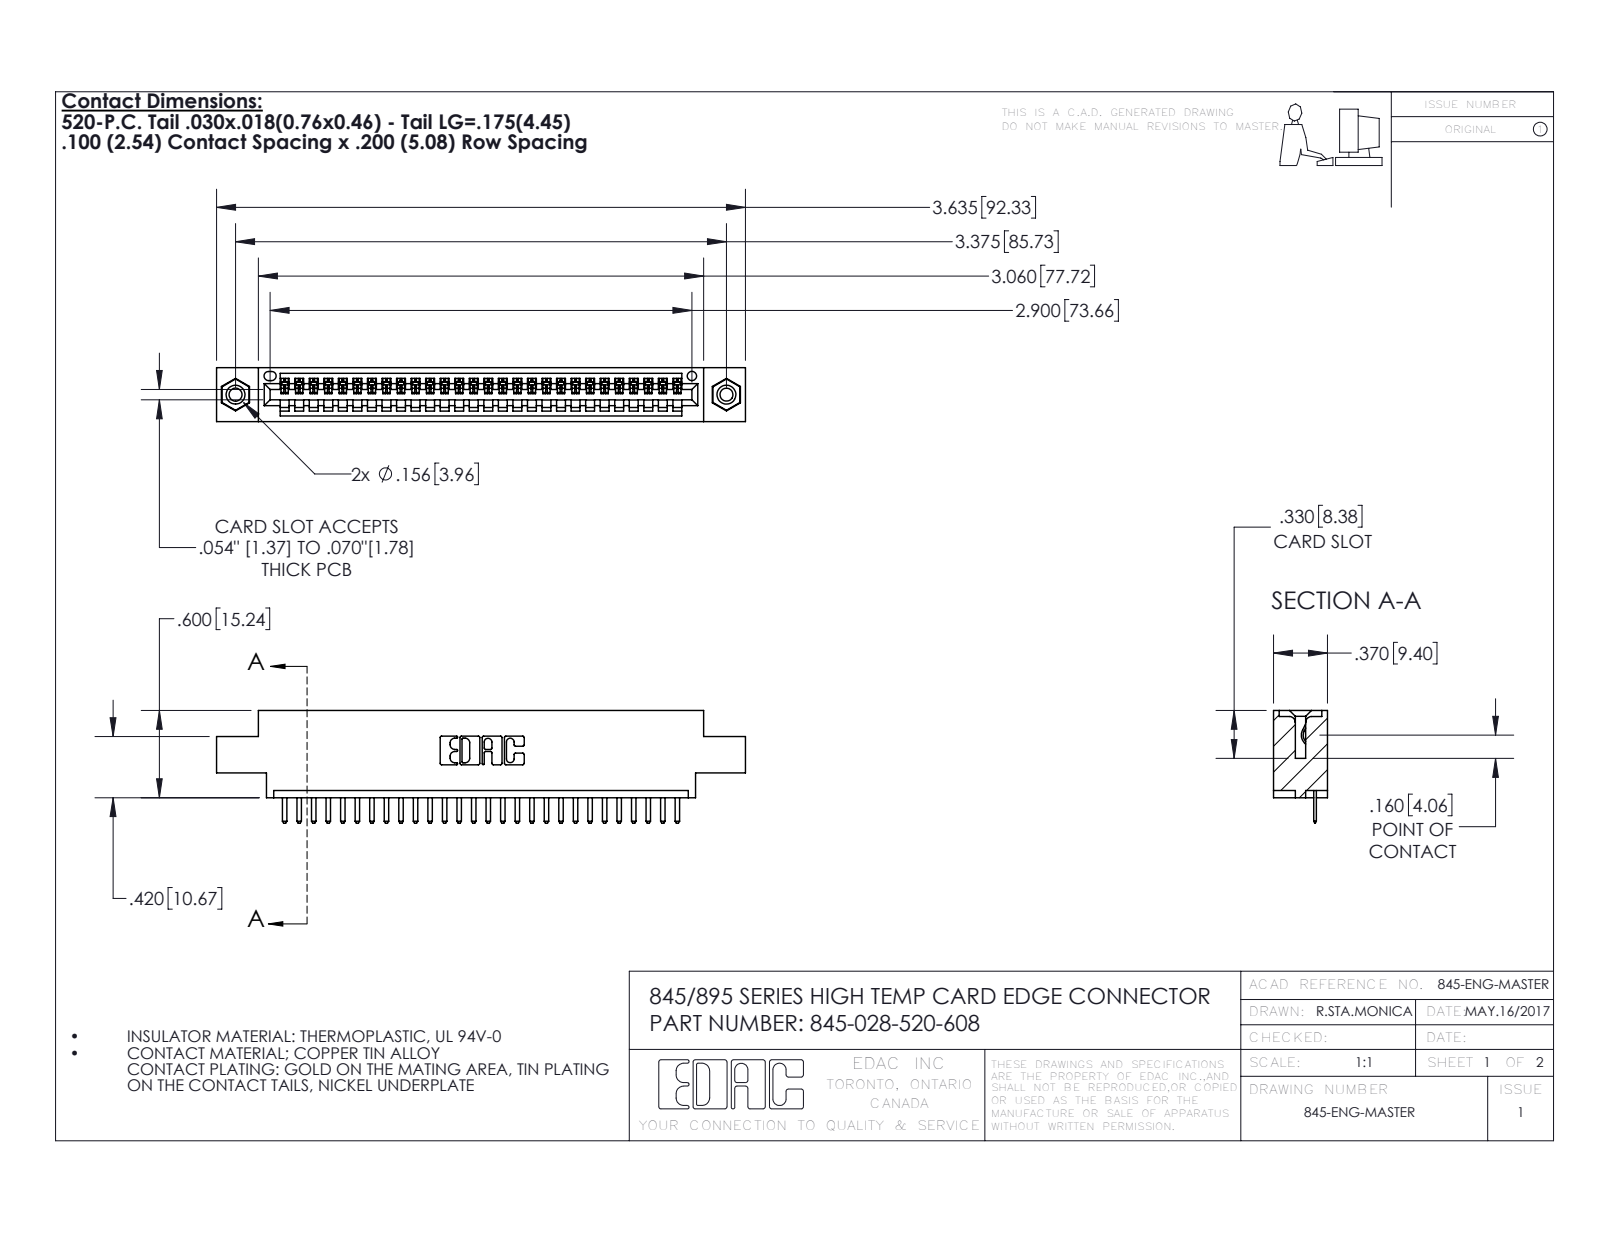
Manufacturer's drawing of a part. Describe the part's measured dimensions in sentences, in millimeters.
The part is named "345-292-001_345-293-120; 345-028-520-608; 345-250-001_345-250-003-102; 345 Part_0.170 Offset - 0.156 Dia-TI". Its 3-D file was written by "SolidWorks 2016 (CONFIG_CONTROL_DESIGN)". It is 31 solids with 1926 faces: 1292 planar, 618 cylindrical and 16 other. Overall it measures 92.3 by 19.7 by 9.4 millimeters. Its volume is 8 460 cubic millimeters and its surface area 10 930 square millimeters. Round holes: 2 of diameter 2.3, 2 of diameter 3.2, 2 of diameter 4, 1 of diameter 1.6. Round bosses or shafts: 2 of diameter 3.9. Partial cylindrical surfaces (rounded edges, fillets, slot ends): 58 of radius 0.3, 56 of radius 0.2, 22 of radius 0.3, 6 of radius 0.2, 6 of radius 0.8, 3 of radius 0.7, 2 of radius 0.8, 2 of radius 1. The main face-to-face distances are 1.8, 7.6, 9.4, 5.1, 2.5, 6.9, 0.6, 5.7, 1.8, 4.4. The hole center spacings are 6.9, 79.8, 85.7.
